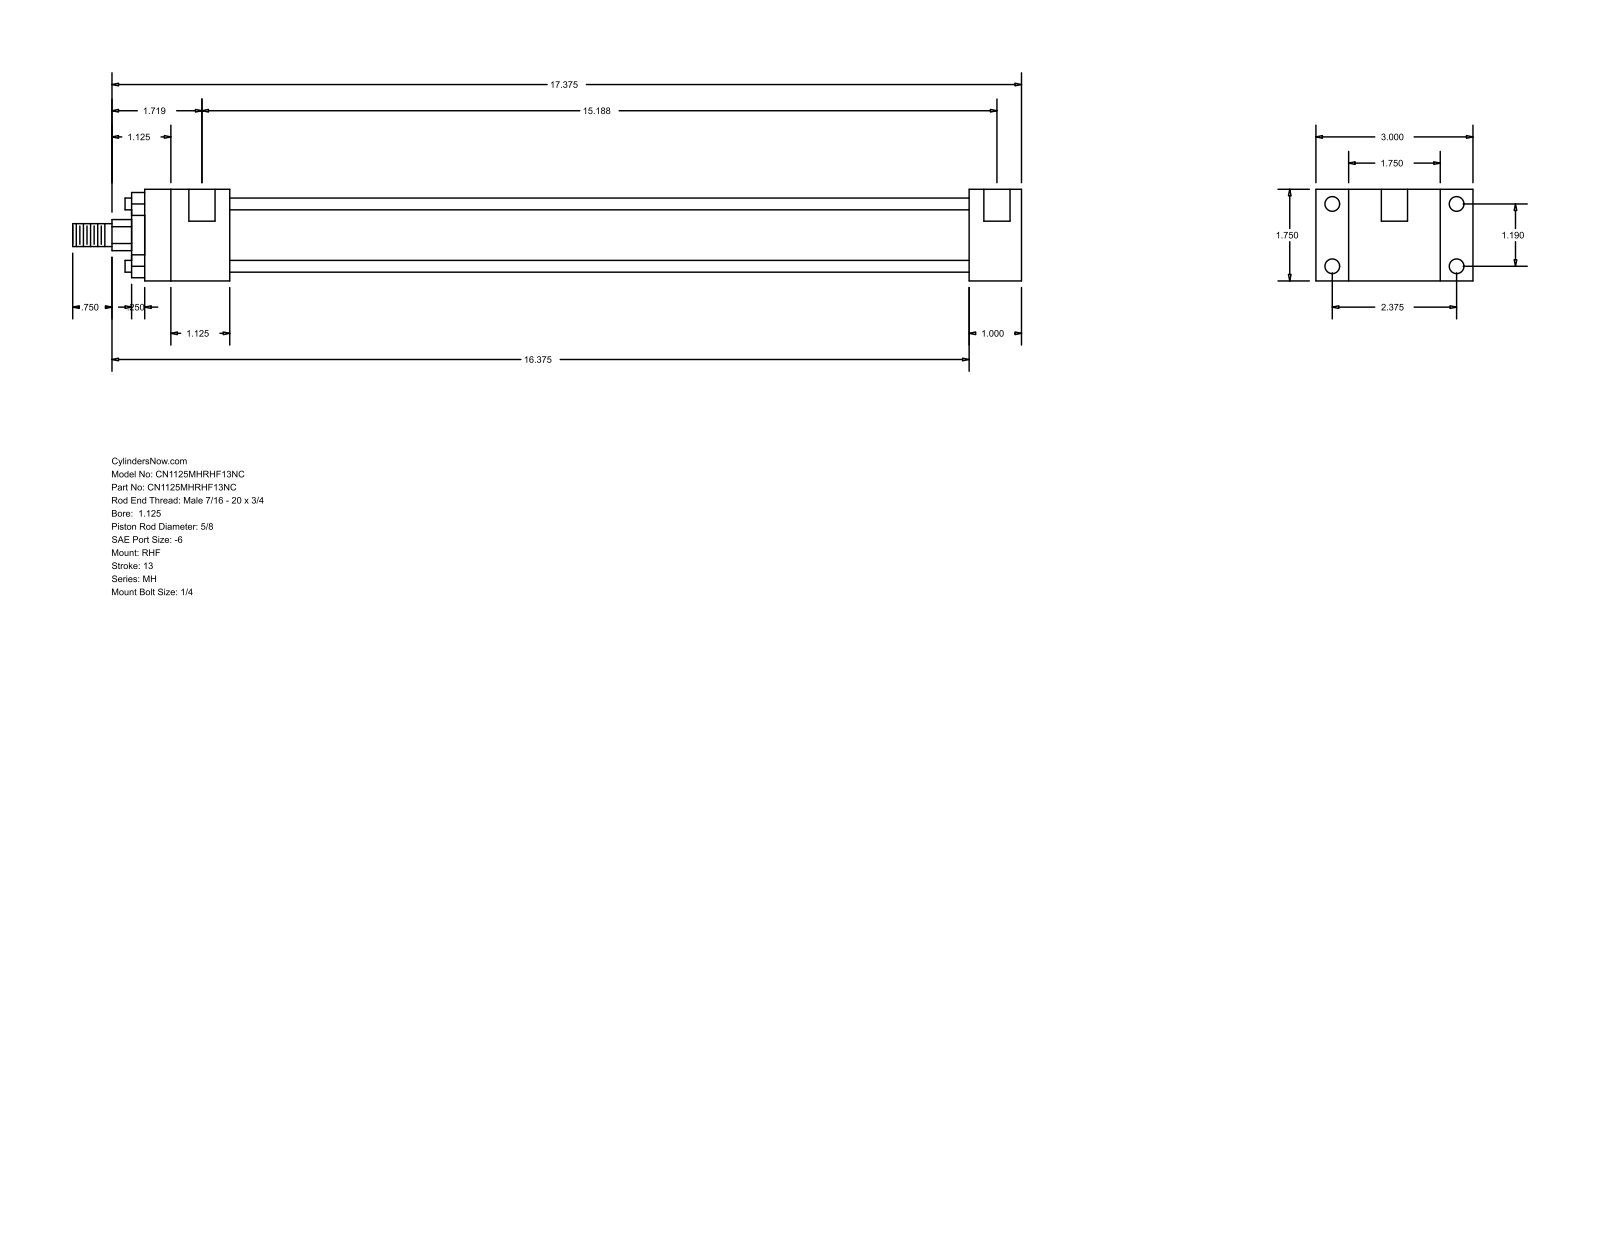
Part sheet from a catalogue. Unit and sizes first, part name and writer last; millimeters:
Units: millimetres
Overall size (bounding box): 460.38 × 76.2 × 44.45
Round holes (diameter × count): ⌀5.56 ×4, ⌀7.14 ×4, ⌀12.7 ×2
Round bosses / shafts (diameter × count): ⌀5.71 ×4, ⌀34.92 ×1, ⌀28.57 ×1, ⌀15.88 ×1, ⌀11.11 ×1
Partial cylindrical surfaces — rounded edges, fillets, slot ends (radius × count): R7.54 ×1
Main face-to-face distances: 44.46, 15.87, 60.33, 25.39, 76.2, 358.78, 384.17, 41.27, 400.05, 425.44
Hole centre spacings: 30.22, 60.32, 67.47, 382.59, 3.17, 385.76
Bodies: 0 solids, 88 faces (60 planar, 28 cylindrical, 0 other)
Part name (STEP PRODUCT): MH_RHF__0112_0.625
STEP written by: GSSL Pune (CONFIG_CONTROL_DESIGN)
